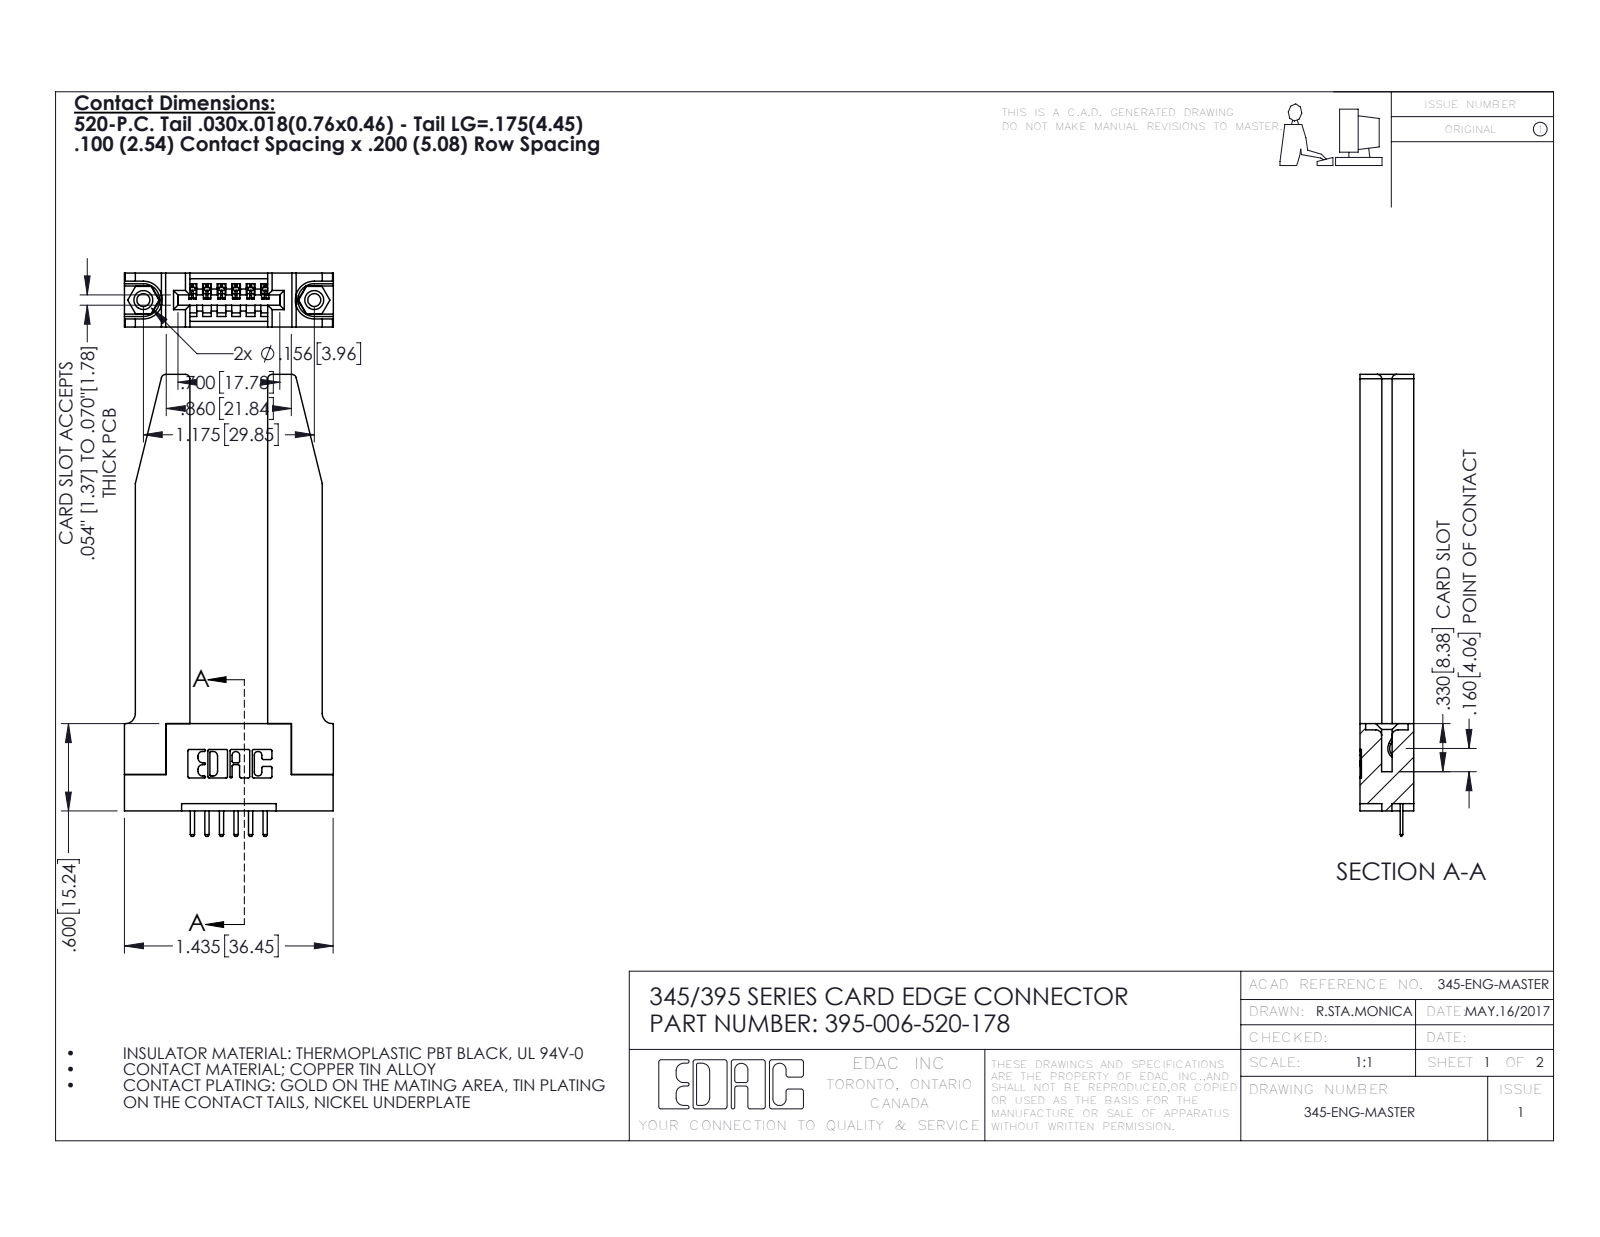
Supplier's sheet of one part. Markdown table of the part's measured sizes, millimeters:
| quantity | value |
| --- | --- |
| part name | 345-250-001_345-250-001-102; 395-006-520-178; 345-292-001_345-293-120; 345 Part_Flush Mounting Lugs - 0.156 Dia-TH (+1 more) |
| STEP written by | SolidWorks 2016 (CONFIG_CONTROL_DESIGN) |
| units | millimeters |
| bodies | 11 solids, 732 faces (474 planar, 206 cylindrical, 52 other) |
| overall size | 80.6 × 36.5 × 9.4 |
| volume | 10 900 mm³ |
| surface area | 10 490 mm² |
| round holes (diameter × count) | 2.3 × 2, 3.2 × 2, 4 × 2, 1.6 × 1 |
| round bosses / shafts (diameter × count) | 3.9 × 2 |
| partial cylindrical surfaces (radius × count) | 0.3 × 22, 0.3 × 14, 0.2 × 12, 0.8 × 8, 0.2 × 6, 0.8 × 6, 0.7 × 3, 0.8 × 2 |
| main face-to-face distances | 9.4, 3.8, 5.6, 13.6, 1.8, 3.8, 2, 7.6, 5.1, 2.4 |
| hole center spacings | 6.9, 24, 29.8 |
